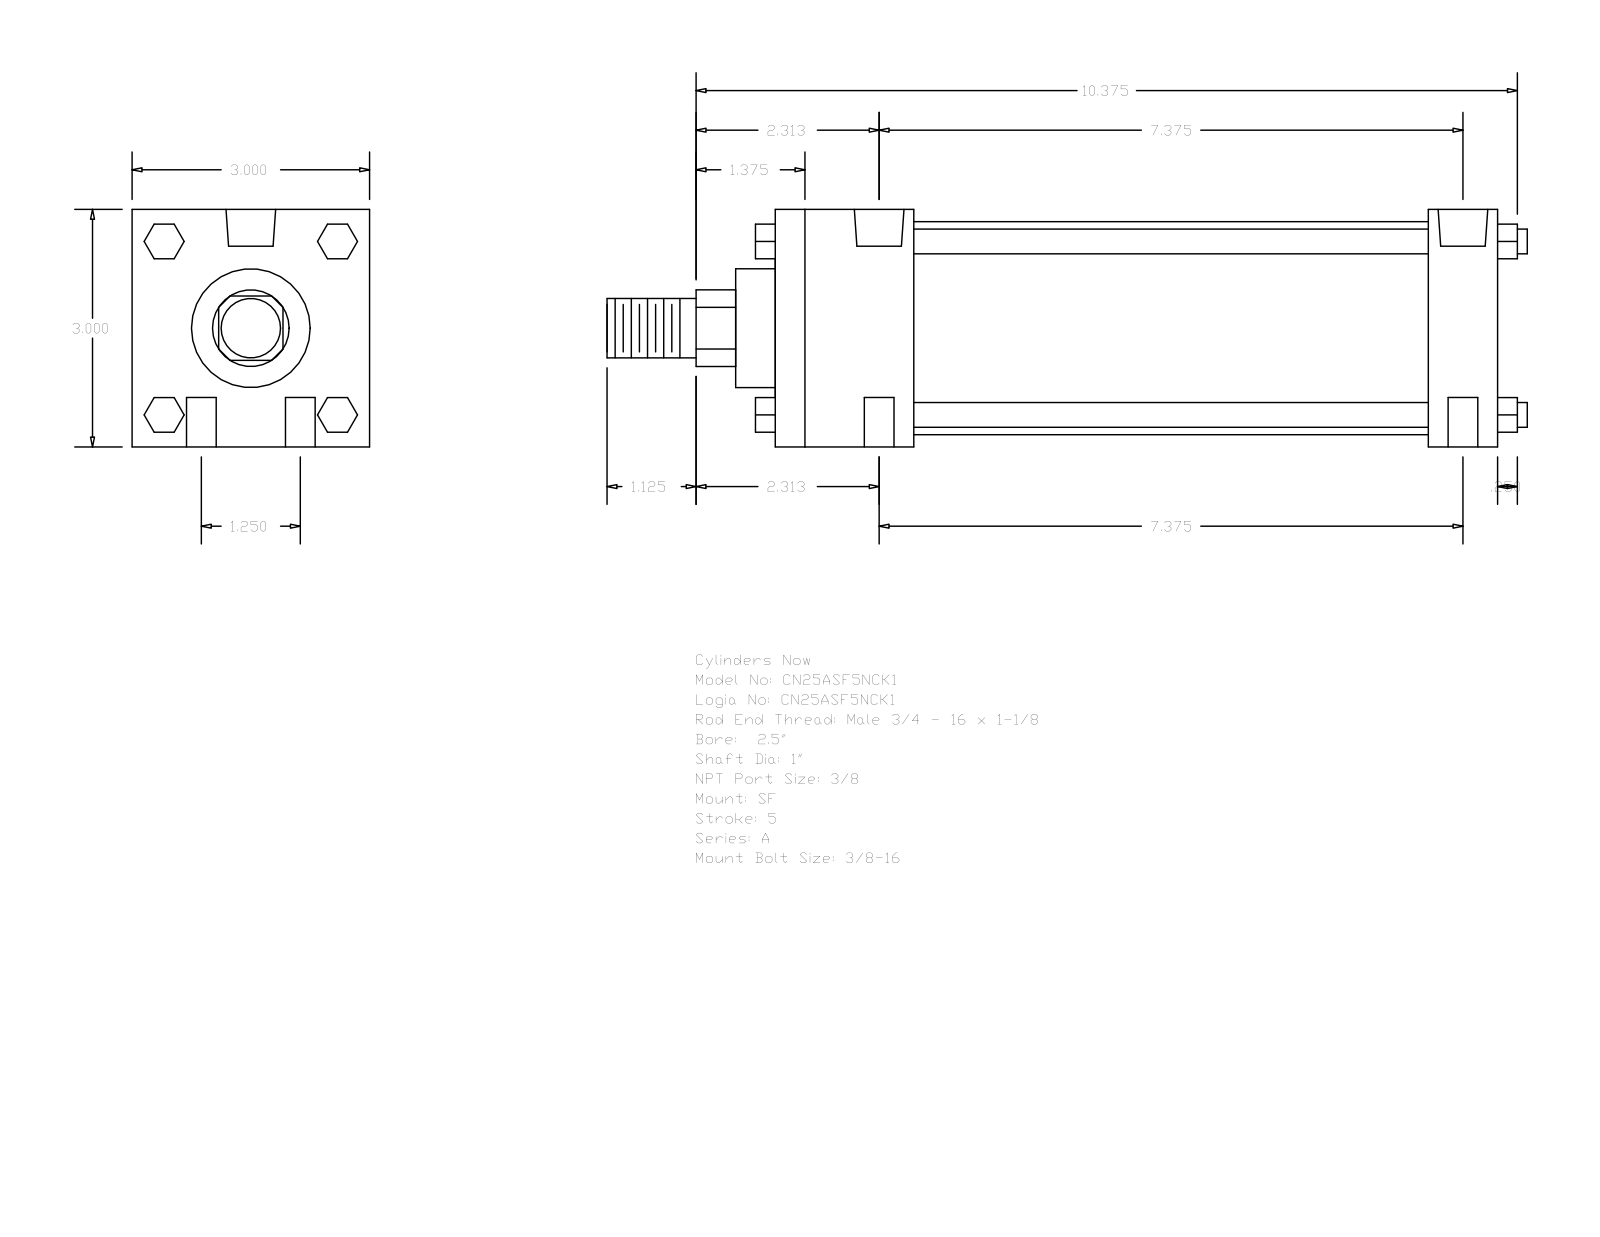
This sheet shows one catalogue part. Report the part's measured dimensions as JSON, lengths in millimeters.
{"part_name": "A_SF__0250_1", "step_written_by": "GSSL Pune (CONFIG_CONTROL_DESIGN)", "units": "millimeters", "bodies": {"solids": 0, "faces": 124, "planar": 94, "cylindrical": 30, "other": 0}, "overall_size": [295.27, 76.2, 76.2], "round_holes": [[9.53, 4], [5.56, 2], [15.93, 2]], "round_bosses_or_shafts": [[7.94, 4], [68.33, 1], [38.1, 1], [25.4, 1], [19.05, 1]], "partial_cylinders_radius": [[12.29, 1]], "face_to_face_distances": [76.2, 231.78, 209.55, 22.23, 44.45, 165.1, 187.33, 12.7, 11.11, 57.15], "hole_center_spacings": [15.88, 187.99, 187.32, 31.76, 189.99, 192.08]}
